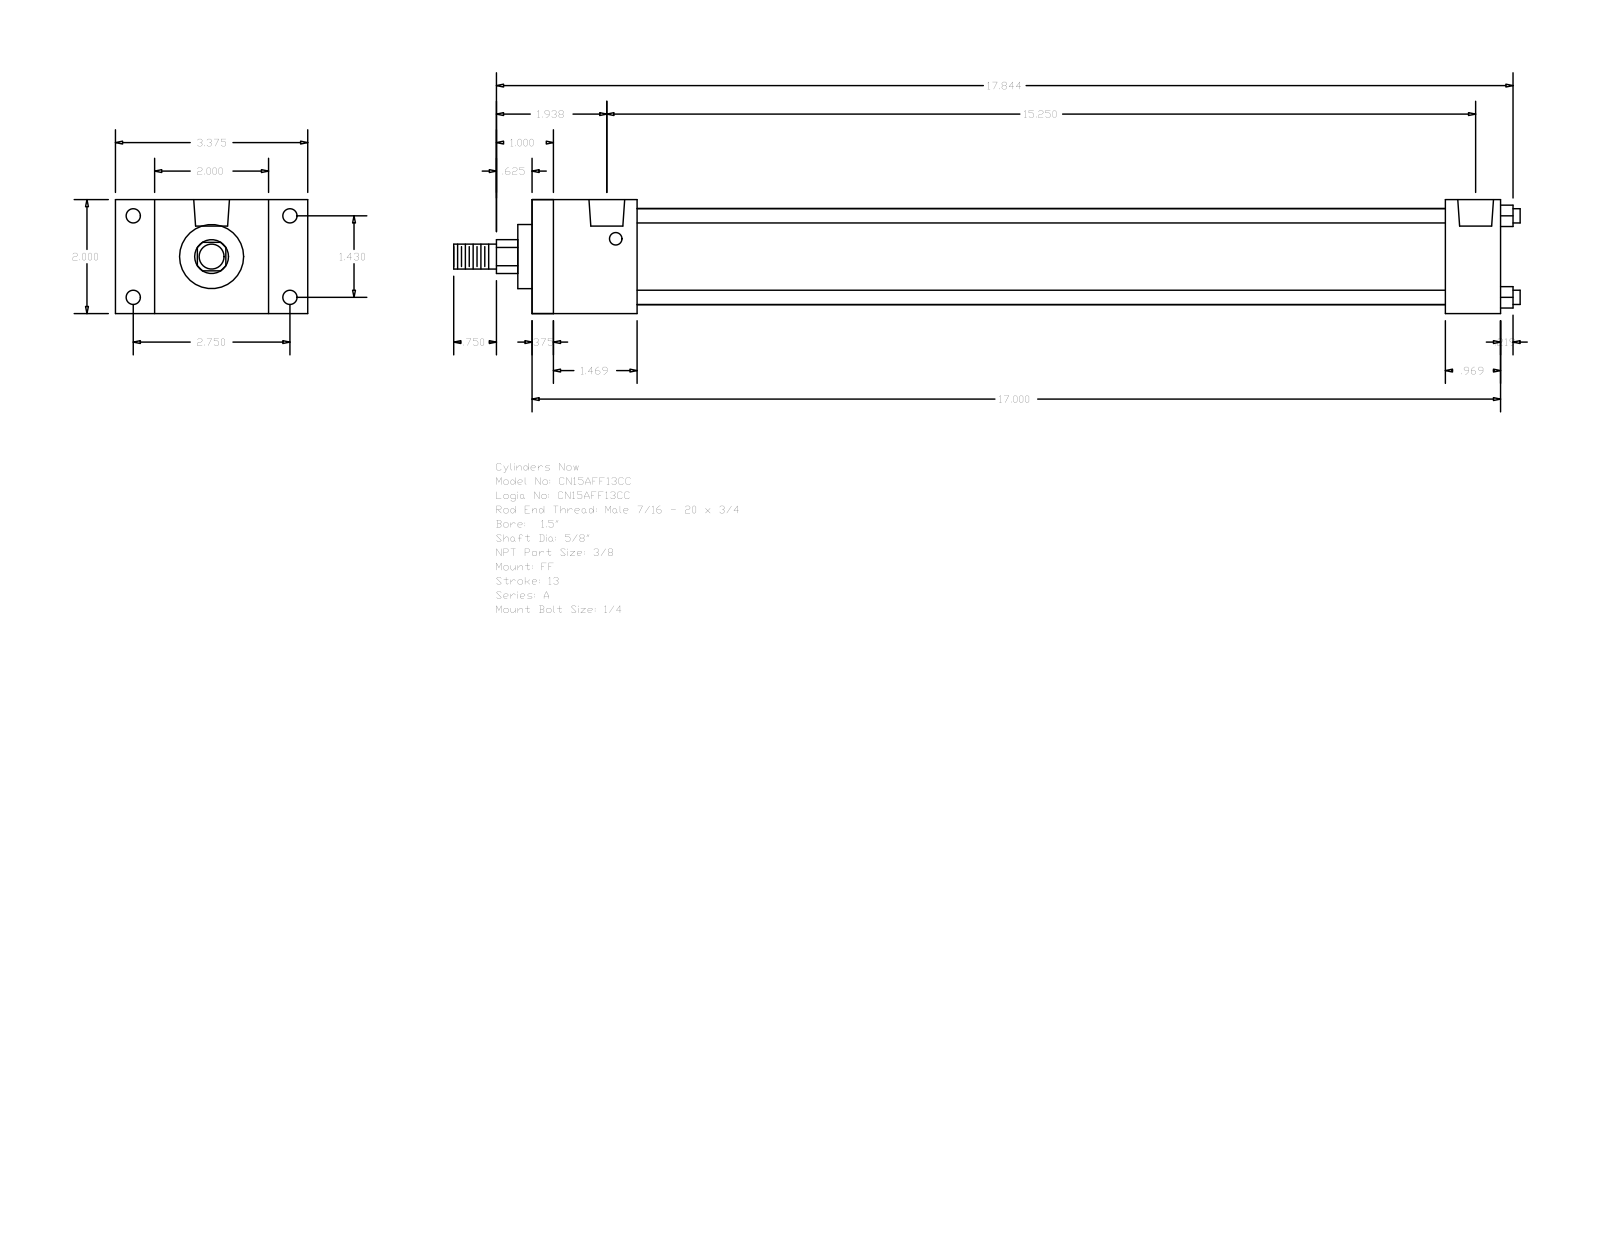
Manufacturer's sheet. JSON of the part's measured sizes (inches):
{"part_name": "A_FF__0150_0.625", "step_written_by": "GSSL Pune (CONFIG_CONTROL_DESIGN)", "units": "inches", "bodies": {"solids": 0, "faces": 92, "planar": 64, "cylindrical": 28, "other": 0}, "overall_size": [18.719, 3.375, 2], "round_holes": [[0.219, 4], [0.25, 4], [0.627, 2]], "round_bosses_or_shafts": [[0.25, 4], [1.69, 1], [1.125, 1], [0.625, 1], [0.437, 1]], "partial_cylinders_radius": [[0.297, 1]], "face_to_face_distances": [2, 17, 0.375, 16.625, 1.844, 16.031, 1.469, 15.656, 14.187, 15.156], "hole_center_spacings": [0.156, 1.43, 2.75, 3.099, 14.937, 15.094, 15.25]}
